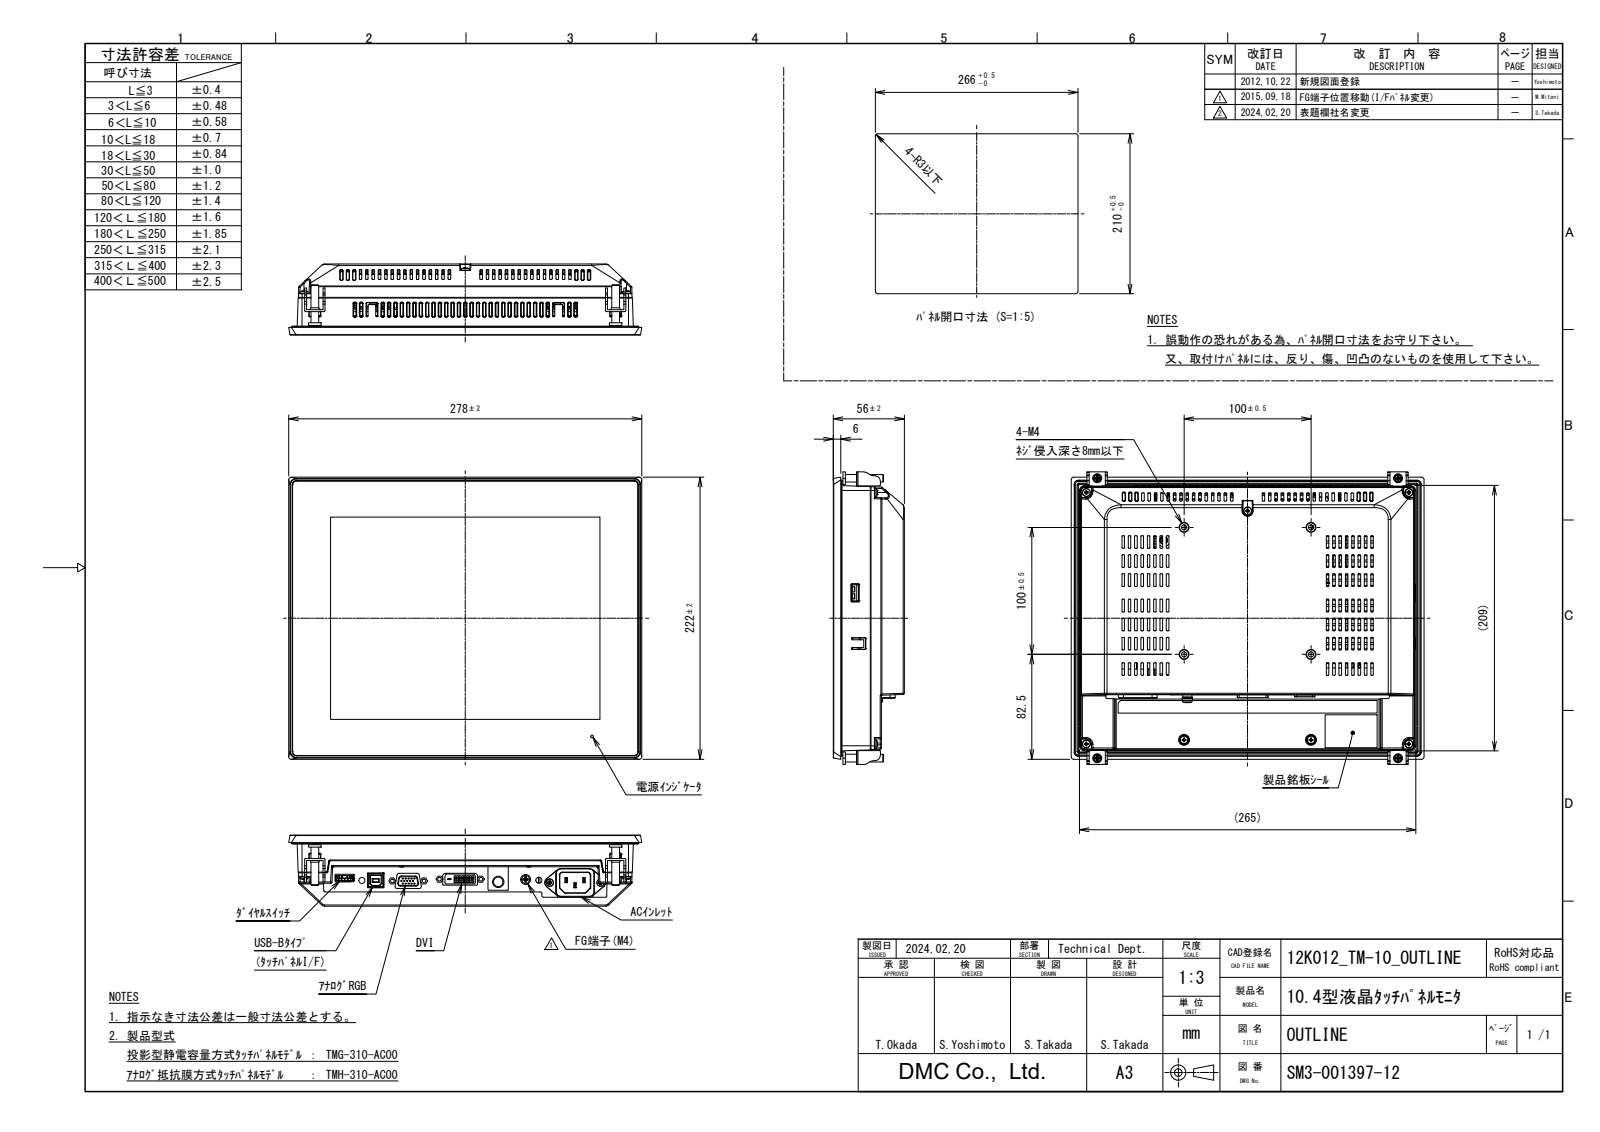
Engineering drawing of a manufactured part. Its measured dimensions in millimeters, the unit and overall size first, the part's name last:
Units: millimetres
Overall size (bounding box): 278 × 230.29 × 56
Round holes (diameter × count): ⌀3.5 ×118, ⌀3 ×32, ⌀8 ×18, ⌀1 ×17, ⌀4 ×15, ⌀3.2 ×7, ⌀4.5 ×6, ⌀3.8 ×4, ⌀4.8 ×4, ⌀9 ×4, ⌀10 ×4, ⌀2.6 ×2
Round bosses / shafts (diameter × count): ⌀3 ×13, ⌀6.15 ×12, ⌀4 ×11, ⌀6.2 ×8, ⌀7.15 ×6, ⌀3.6 ×6, ⌀10 ×4, ⌀7 ×4
Partial cylindrical surfaces — rounded edges, fillets, slot ends (radius × count): R0.5 ×190, R1 ×115, R0.3 ×107, R1.3 ×18, R0.1 ×17, R2 ×16, R1.1 ×13, R1.6 ×12
Main face-to-face distances: 1, 27.7, 3, 20.1, 21.1, 19.85, 18.85, 1.25, 7, 8
Hole centre spacings: 2.29, 3.96, 6.05, 2.28, 4.58, 4.57, 5, 10
Volume: 557 254 mm³ · Surface area: 606 074 mm²
Bodies: 5 solids, 6357 faces (3642 planar, 1211 cylindrical, 1504 other)
Part name (STEP PRODUCT): HP_TMG(H)-310-AC00
STEP written by: Autodesk Inventor 2017 (CONFIG_CONTROL_DESIGN)
